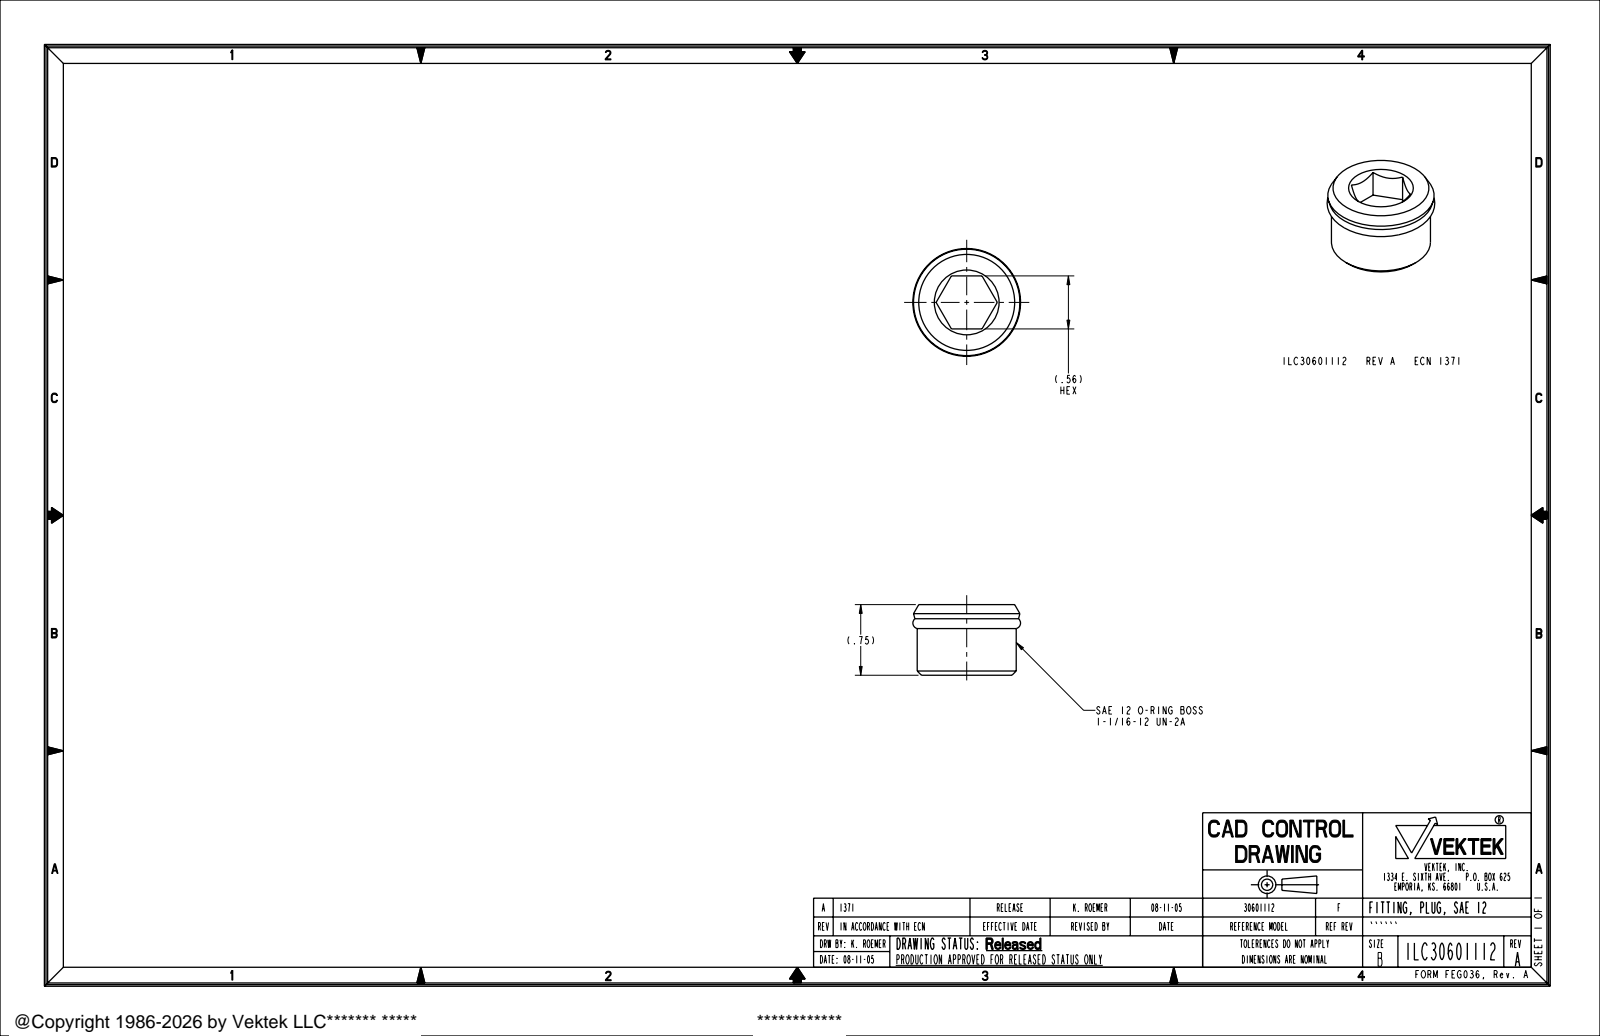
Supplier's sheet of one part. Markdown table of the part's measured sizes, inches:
| quantity | value |
| --- | --- |
| part name | ILC30601112 |
| STEP written by | PRO/ENGINEER BY PARAMETRIC TECHNOLOGY CORPORATION, 2004290 (AUTOMOTIVE_DESIGN_CC2) |
| units | inches |
| bodies | 1 solid, 21 faces (9 planar, 2 cylindrical, 10 other) |
| overall size | 1.144 × 1.144 × 0.75 |
| volume | 0.583 in³ |
| surface area | 4.827 in² |
| round bosses / shafts (diameter × count) | 1.052 × 1 |
| main face-to-face distances | 0.75, 0.437, 0.313, 0.563 |
